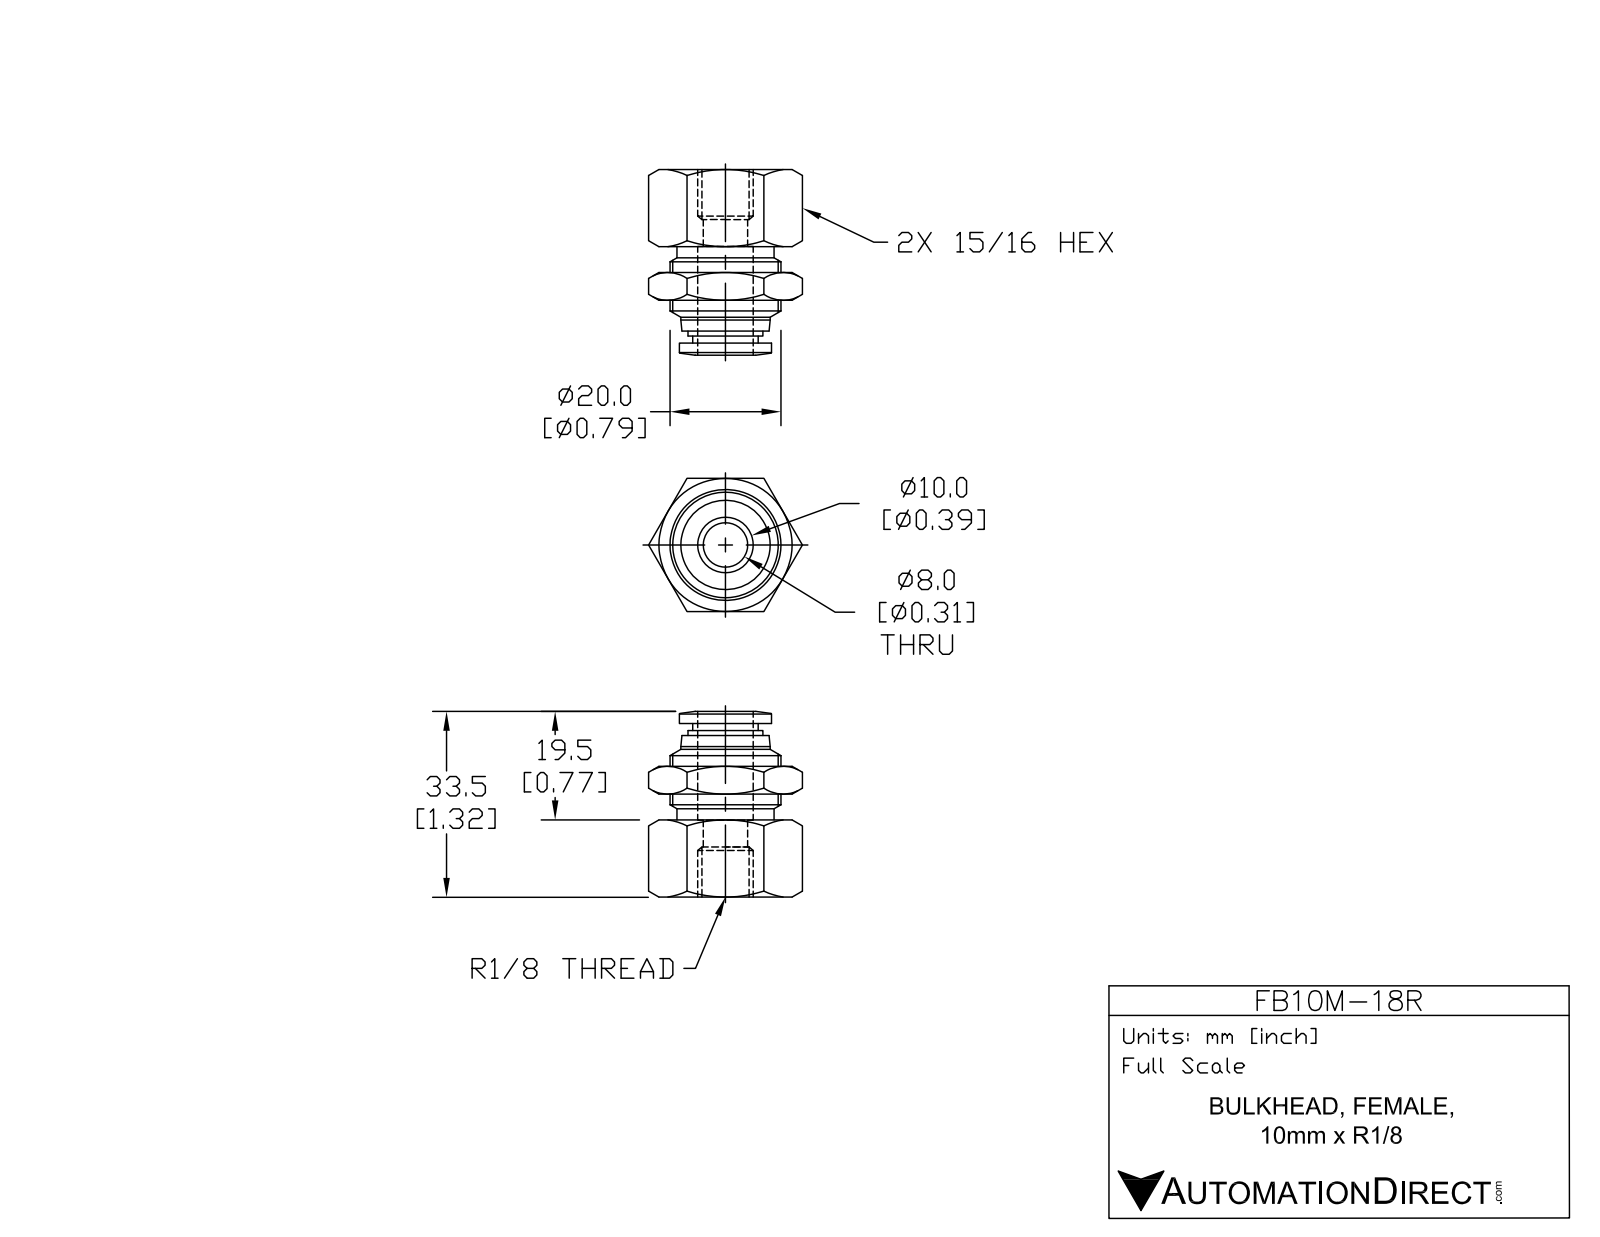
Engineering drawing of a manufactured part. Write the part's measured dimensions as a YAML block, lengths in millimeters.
part_name: "FB10M-18R"
step_written_by: "SolidWorks 2015 (AUTOMOTIVE_DESIGN)"
units: millimeters
bodies: {solids: 1, faces: 82, planar: 22, cylindrical: 18, other: 42}
overall_size: [33.6, 27.7, 24]
volume: 10300
surface_area: 4801
round_holes:
  - {diameter: 8, count: 1}
  - {diameter: 10.3, count: 1}
round_bosses_or_shafts:
  - {diameter: 20, count: 1}
  - {diameter: 17.5, count: 1}
  - {diameter: 16.6, count: 1}
  - {diameter: 16.1, count: 1}
  - {diameter: 13.5, count: 1}
  - {diameter: 11.8, count: 1}
face_to_face_distances: [24, 14, 5, 9.6, 18.6, 4.6, 23.6, 31.3, 17.3, 12.8]
